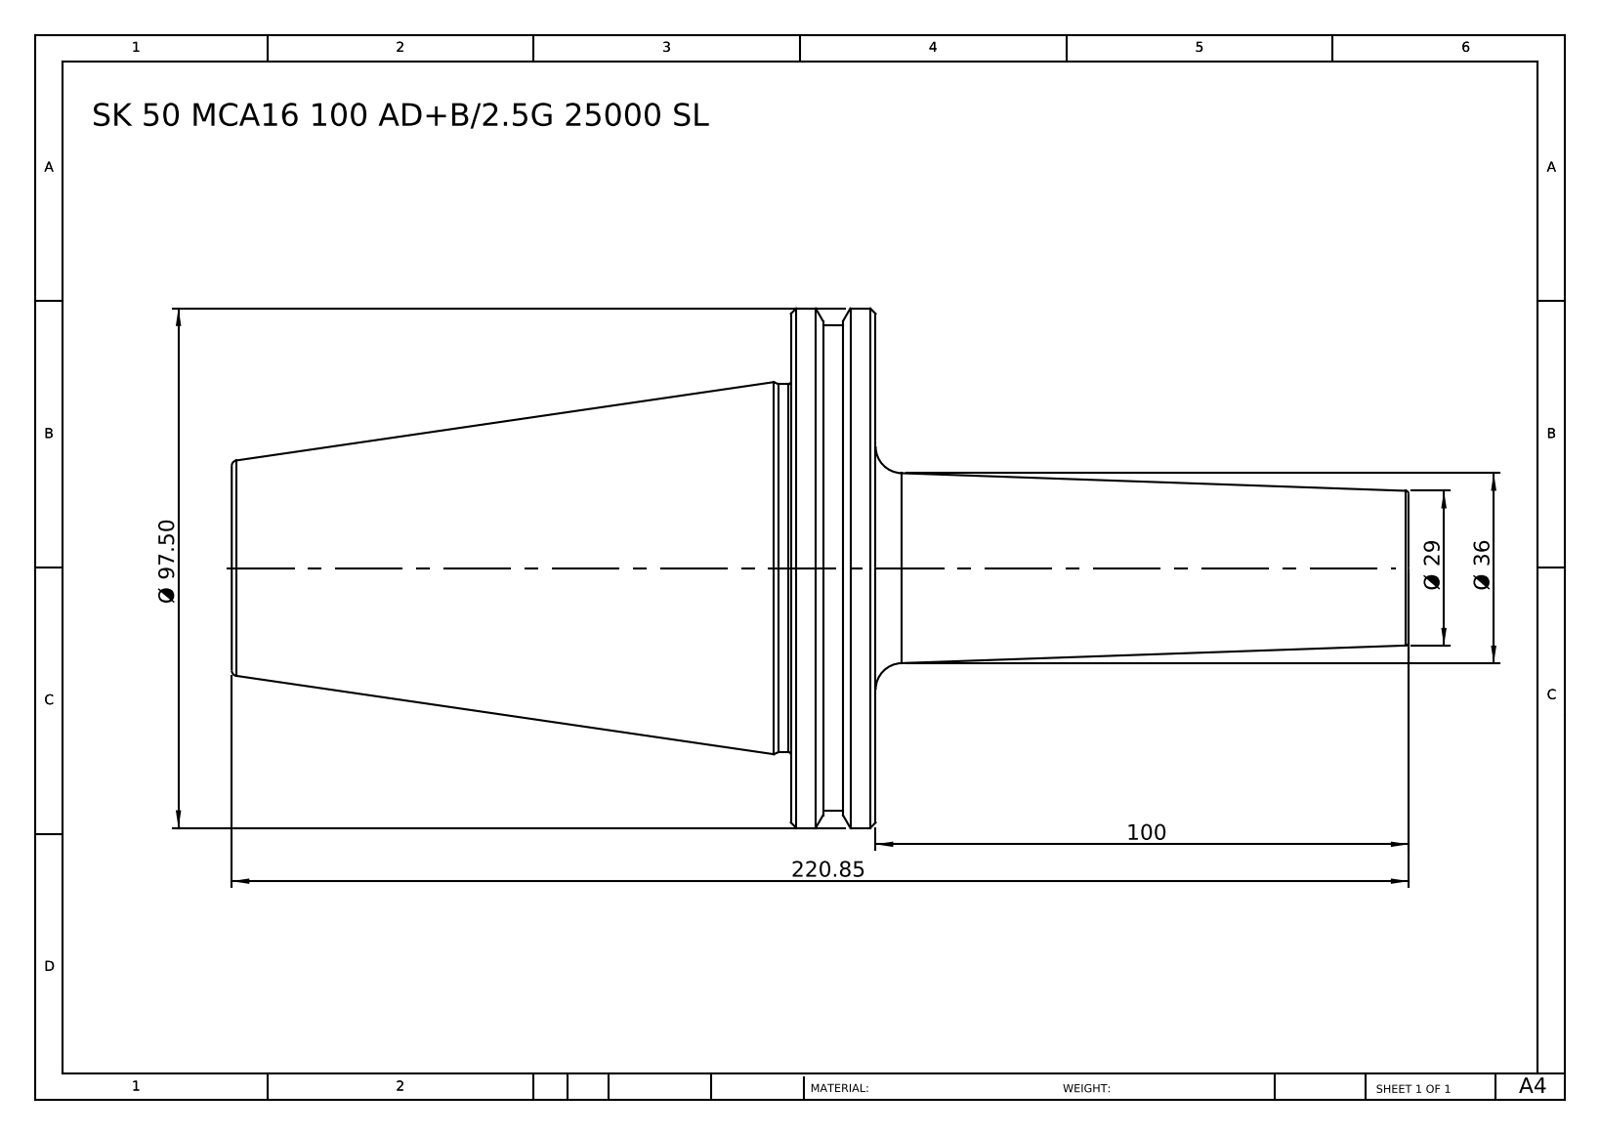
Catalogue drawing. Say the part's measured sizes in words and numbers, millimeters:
The part is named "SK 50 MCA16 100 AD+B-2.5G25000 SL". Its 3-D file was written by "SolidWorks 2014 (CONFIG_CONTROL_DESIGN)". It is 1 solid with 36 faces: 6 planar, 8 cylindrical and 22 other. Overall it measures 220.85 by 97.5 by 97.5 millimeters. Its volume is 457 408 cubic millimeters and its surface area 46 229 square millimeters. Round bosses or shafts: 1 of diameter 97.5, 1 of diameter 91, 1 of diameter 69. The main face-to-face distances are 15.9, 120.85, 104.95, 100, 115.9, 220.85, 106.13, 6.13, 9.77, 114.72.
